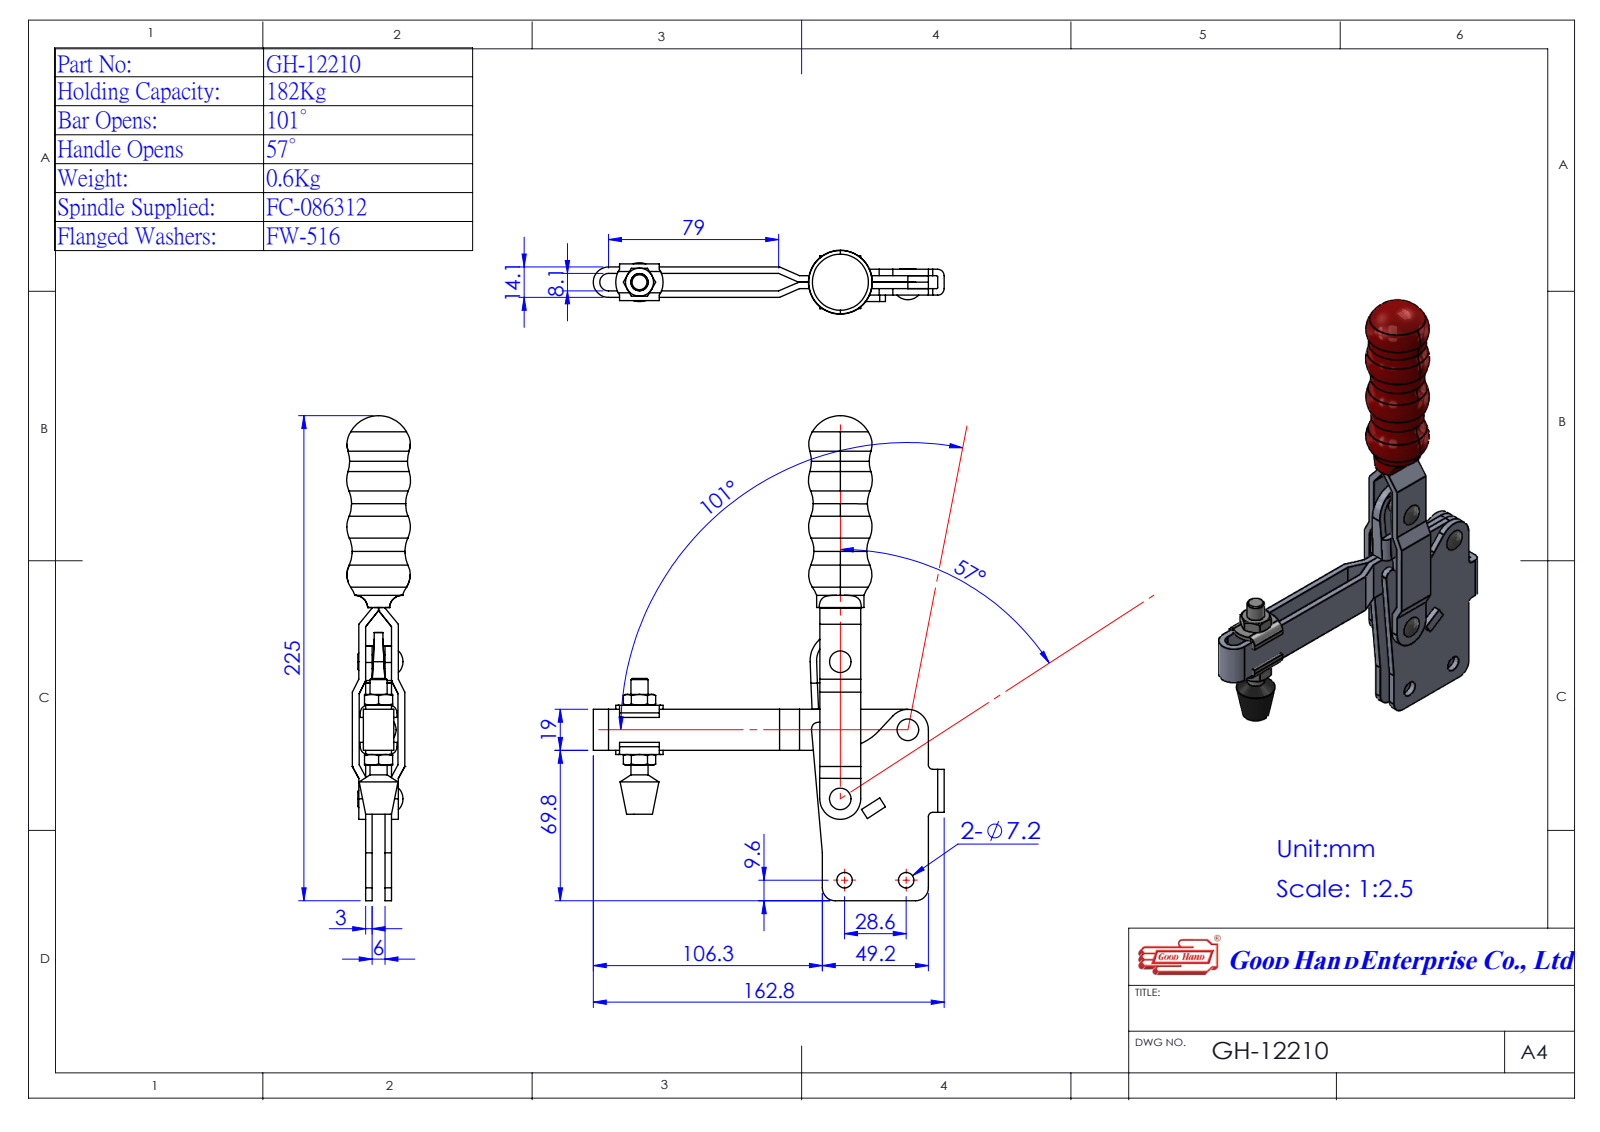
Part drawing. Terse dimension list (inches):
name: Group5^GH-12210(簡化)-1; Group2^GH-12210(簡化)-1; GH-12210(簡化)-1; Group4^GH-12210(簡化)-1 (+2 more)
written by: SolidWorks 2016 (AUTOMOTIVE_DESIGN)
unit: in
bodies: 5 solids, 311 faces (140 planar, 101 cylindrical, 70 other)
size: 8.858 × 6.409 × 1.168
volume: 7.086 in³; area: 89.55 in²
holes: 4× ⌀0.189, 2× ⌀0.283
bosses: 2× ⌀0.248, 1× ⌀0.866, 1× ⌀0.312
rounds: 4× R0.047, 4× R0.118, 4× R0.142, 4× R0.236, 3× R0.126, 2× R0.02, 2× R0.079, 2× R0.285
face distances: 0.118, 0.354, 0.236, 0.472, 0.396, 0.041, 0.159, 0.278, 0.514, 0.077
hole spacings: 2.746, 1.126, 1.181, 1.244, 1.262, 1.487, 1.752, 1.765
